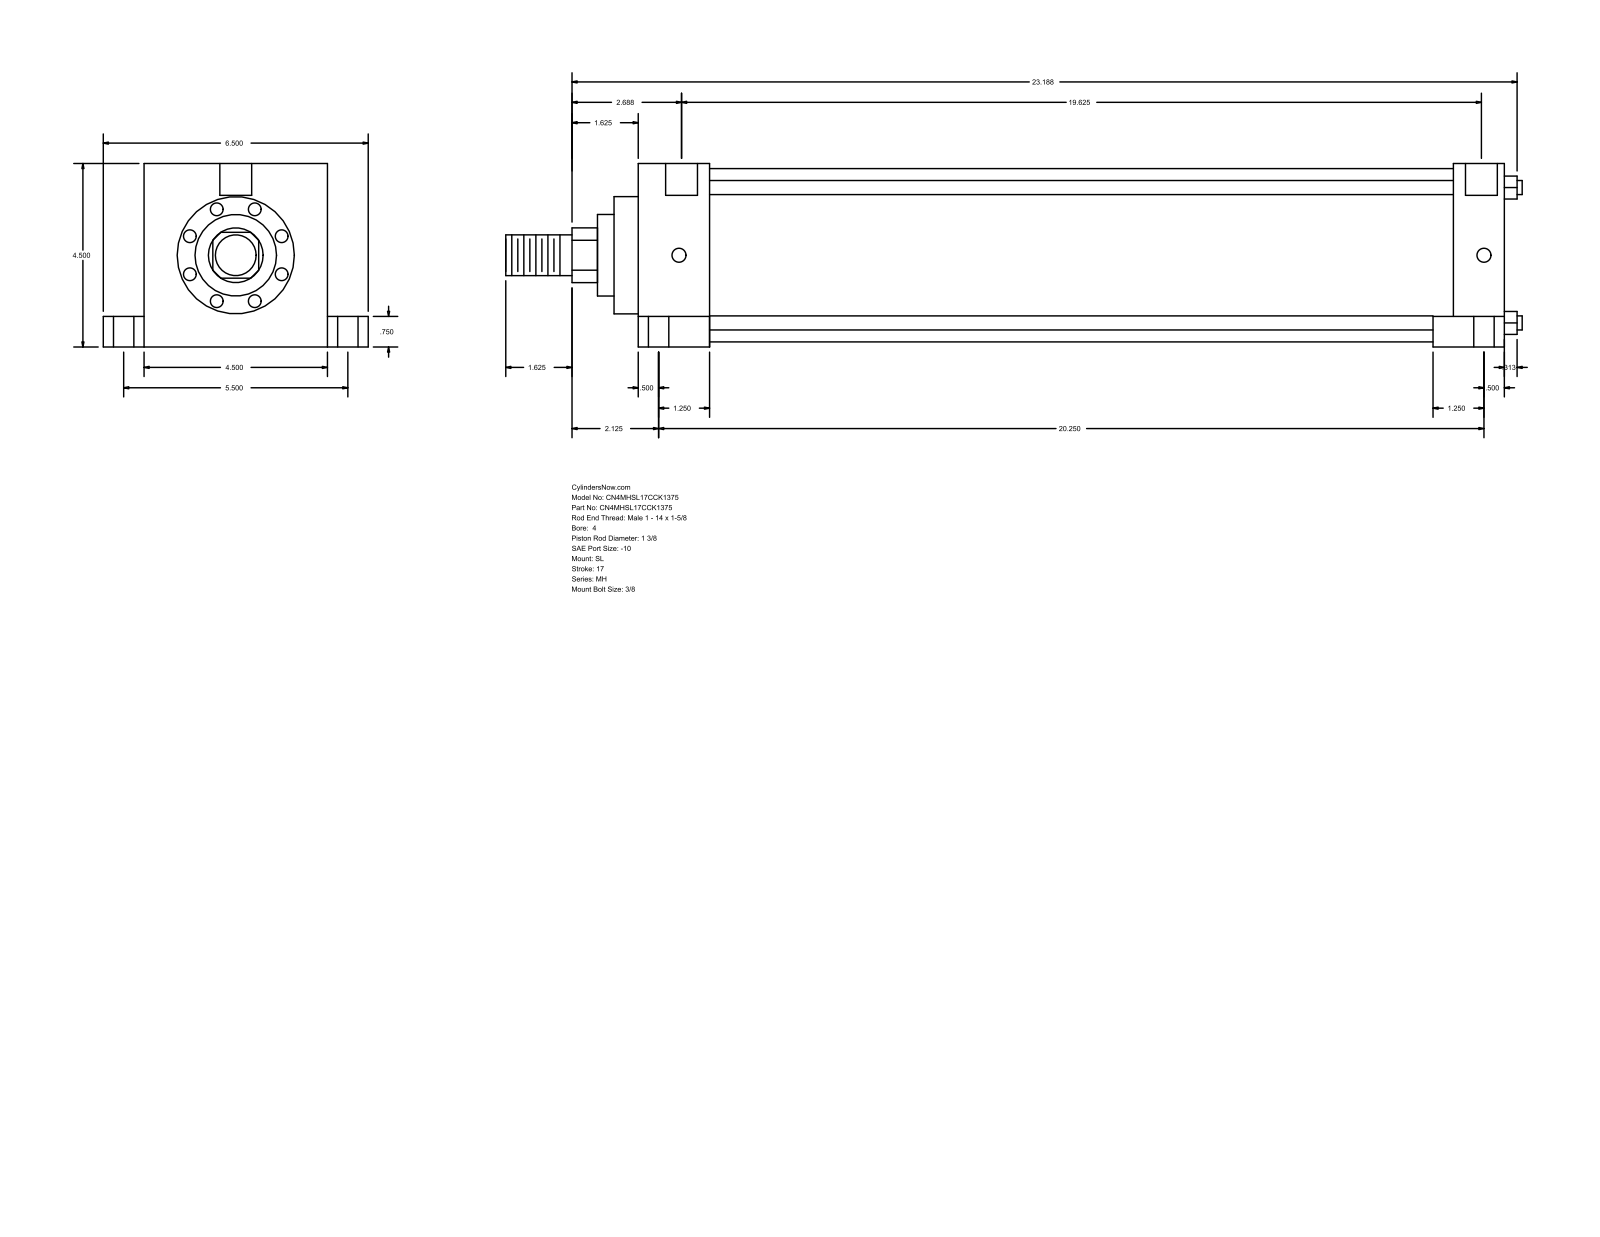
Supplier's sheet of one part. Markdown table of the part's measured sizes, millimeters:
| quantity | value |
| --- | --- |
| part name | MH_SL__0400_1.375 |
| STEP written by | GSSL Pune (CONFIG_CONTROL_DESIGN) |
| units | millimeters |
| bodies | 0 solids, 110 faces (77 planar, 33 cylindrical, 0 other) |
| overall size | 633.41 × 165.1 × 114.3 |
| round holes (diameter × count) | 8.73 × 4, 12.7 × 4, 19.05 × 4, 19.84 × 2 |
| round bosses / shafts (diameter × count) | 8.76 × 4, 107.95 × 1, 73.03 × 1, 50.8 × 1, 34.92 × 1, 25.4 × 1 |
| partial cylindrical surfaces (radius × count) | 17.06 × 1 |
| main face-to-face distances | 114.3, 539.75, 44.45, 495.3, 508, 463.55, 31.75, 25.4, 139.7, 19.05 |
| hole center spacings | 1.59, 69.85, 69.87, 70.99, 71.29, 139.7, 500.07, 501.66 |
